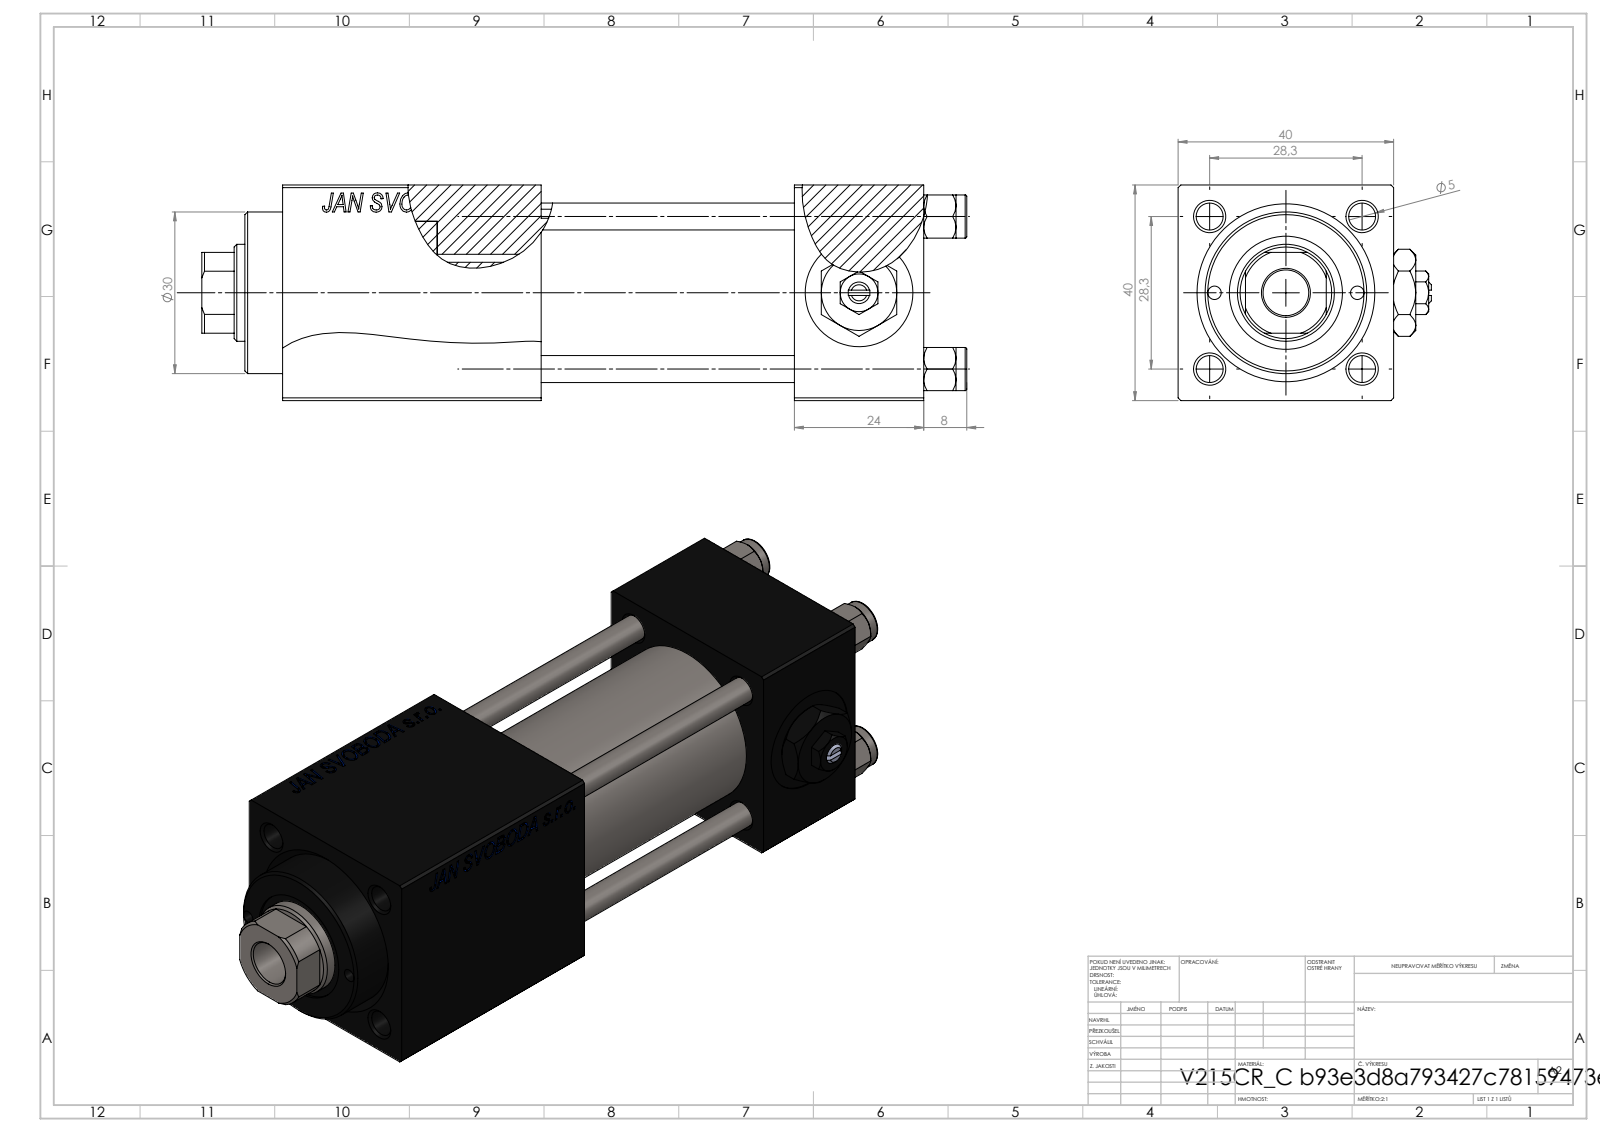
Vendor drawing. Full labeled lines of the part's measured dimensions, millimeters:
Part name (STEP PRODUCT): V215_VC_A; V215CR_C_Body; NUT_M5_C; V215CR_VCP_C (+2 more)
STEP written by: SolidWorks 2019 (CONFIG_CONTROL_DESIGN)
Units: millimetres
Bodies: 12 solids, 1203 faces (549 planar, 96 cylindrical, 558 other)
Overall size (bounding box): 142 × 47 × 40
Volume: 149 125 mm³ · Surface area: 57 930 mm²
Round holes (diameter × count): ⌀5 ×4, ⌀20 ×3, ⌀2.5 ×2, ⌀7 ×2, ⌀13.16 ×2, ⌀8.5 ×1, ⌀18 ×1, ⌀21 ×1, ⌀25 ×1, ⌀30 ×1
Round bosses / shafts (diameter × count): ⌀8 ×4, ⌀31 ×1
Partial cylindrical surfaces — rounded edges, fillets, slot ends (radius × count): R8.5 ×1
Main face-to-face distances: 40, 24, 47, 71, 90.3, 66.3, 19.3, 48, 39.8, 95
Hole centre spacings: 14.18, 20.01, 28.3, 30.84, 13.25, 40.02, 26.5, 72
